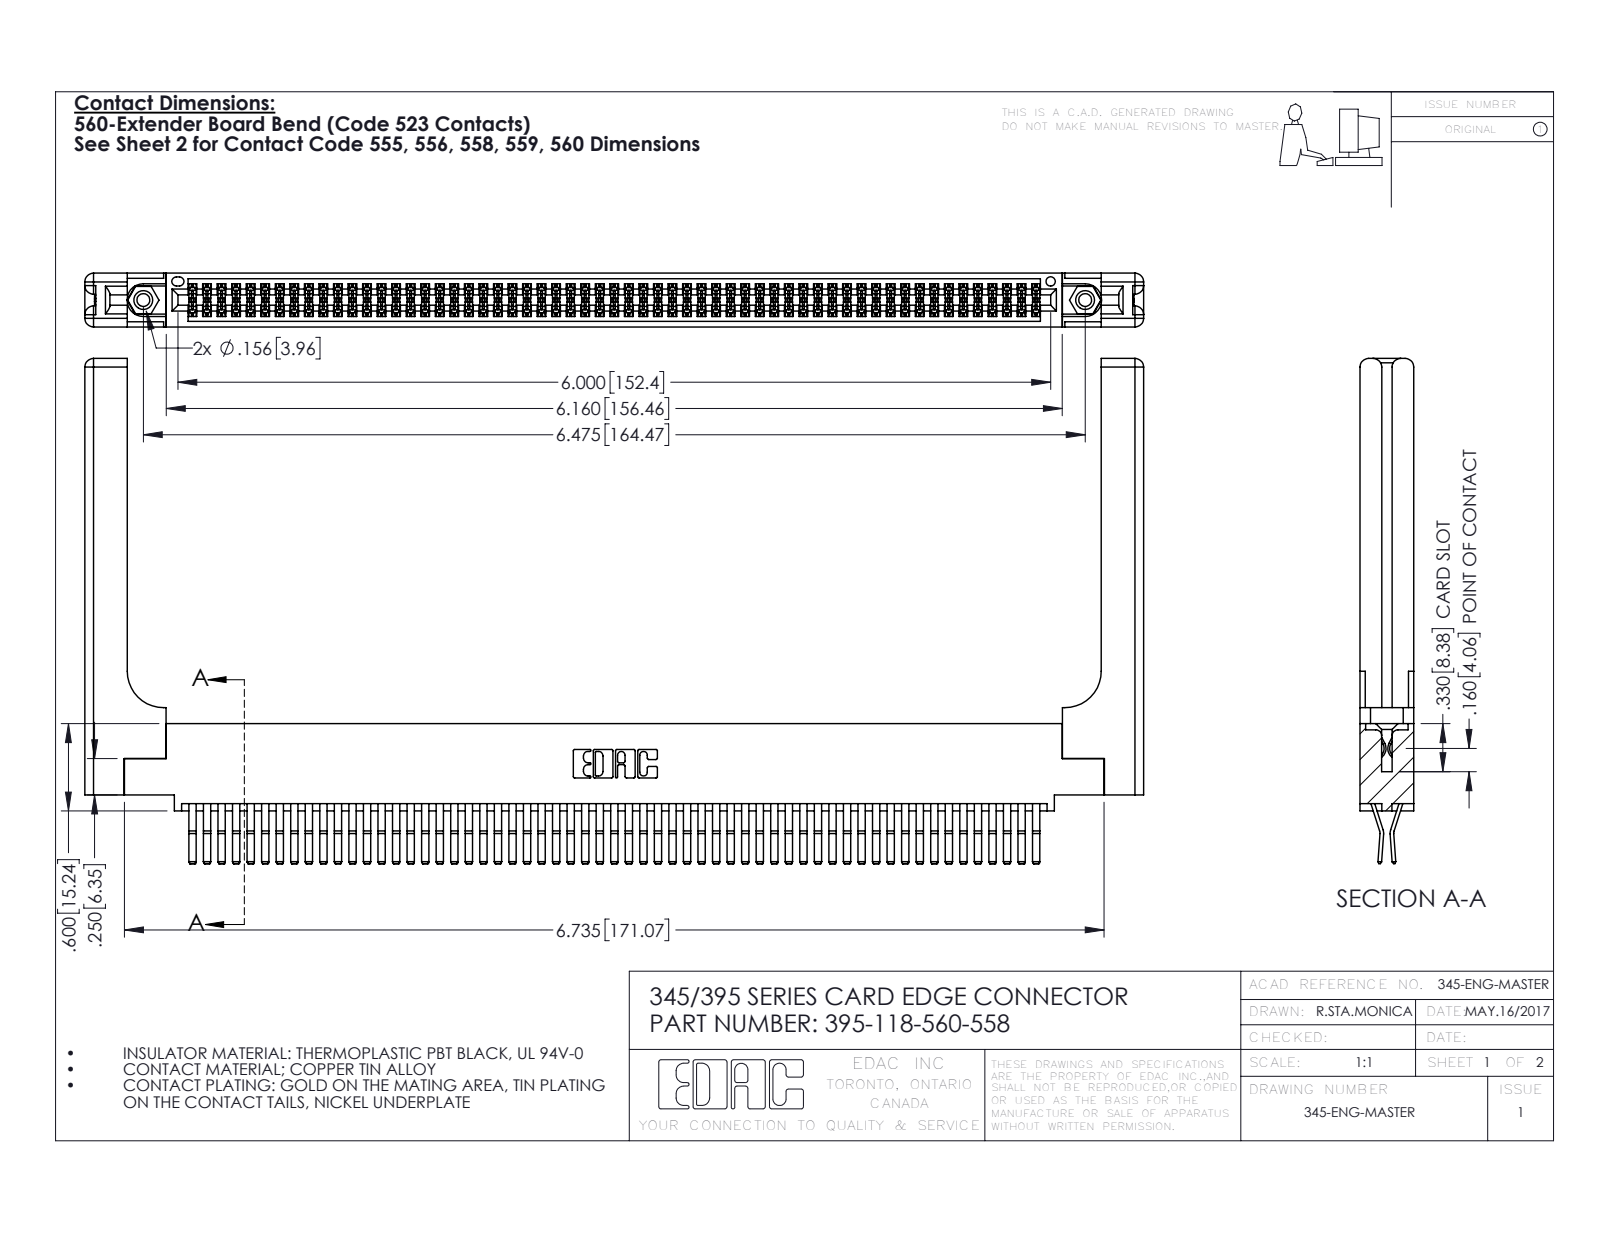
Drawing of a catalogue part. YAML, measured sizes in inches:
part_name: "395-118-560-558; 345-250-001_345-250-001-102; 345-220-058_345-220-058; 345 Part_0.110 Offset - 0.156 Dia-TH (+1 more)"
step_written_by: "SolidWorks 2016 (CONFIG_CONTROL_DESIGN)"
units: inches
bodies: {solids: 123, faces: 6522, planar: 4126, cylindrical: 2336, other: 60}
overall_size: [7.279, 3.472, 0.37]
volume: 1.666
surface_area: 54.69
round_holes:
  - {diameter: 0.089, count: 2}
  - {diameter: 0.125, count: 2}
  - {diameter: 0.156, count: 2}
  - {diameter: 0.064, count: 1}
round_bosses_or_shafts:
  - {diameter: 0.155, count: 2}
partial_cylinders:
  - {radius: 0.006, count: 177}
  - {radius: 0.01, count: 22}
  - {radius: 0.06, count: 16}
  - {radius: 0.007, count: 6}
  - {radius: 0.031, count: 6}
  - {radius: 0.026, count: 3}
  - {radius: 0.01, count: 2}
  - {radius: 0.014, count: 2}
face_to_face_distances: [0.072, 0.298, 0.025, 0.37, 0.098, 0.272, 0.2, 0.225, 0.148, 0.15]
hole_center_spacings: [0.27, 6.239, 6.475]
